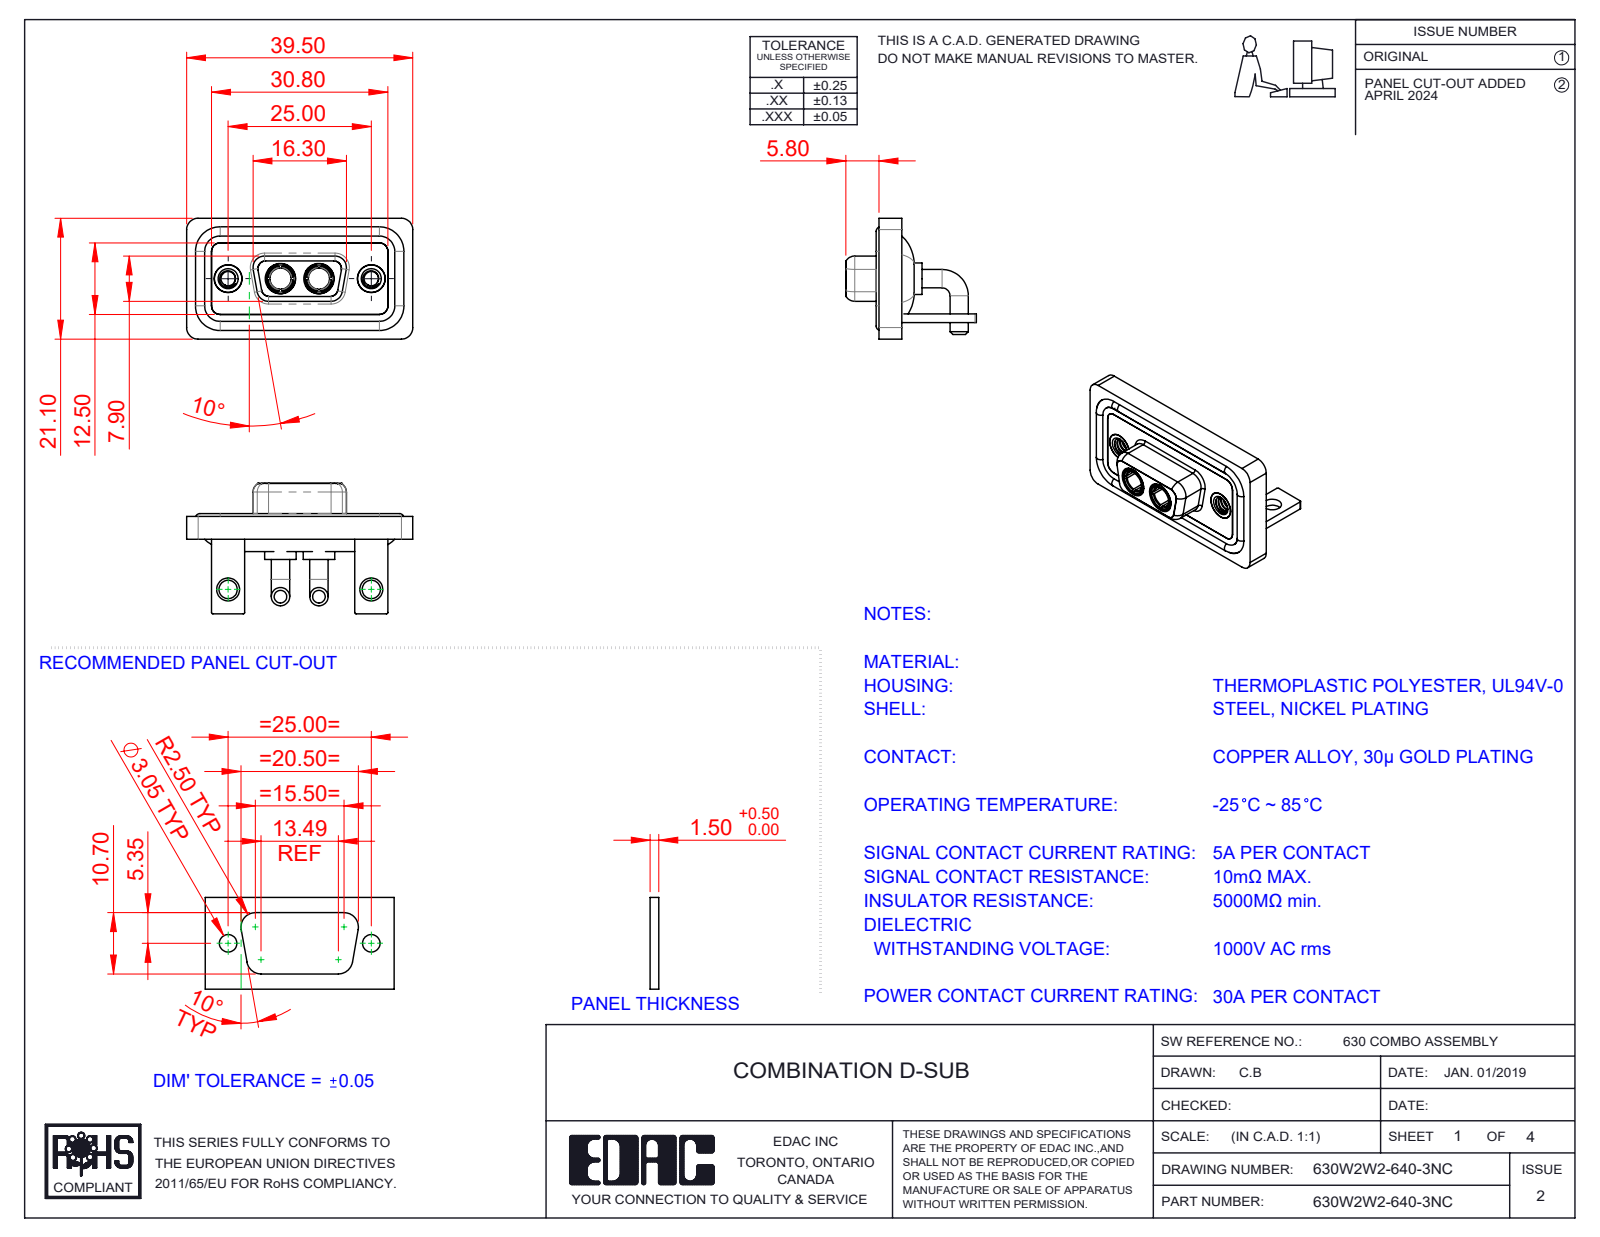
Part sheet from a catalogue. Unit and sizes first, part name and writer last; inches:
Units: inches
Overall size (bounding box): 1.555 × 0.898 × 0.831
Round holes (diameter × count): ⌀0.191 ×4, ⌀0.098 ×2, ⌀0.126 ×2, ⌀0.146 ×2, ⌀0.157 ×2, ⌀0.159 ×2, ⌀0.197 ×2, ⌀0.209 ×2
Round bosses / shafts (diameter × count): ⌀0.126 ×4, ⌀0.063 ×4, ⌀0.217 ×2, ⌀0.205 ×2, ⌀0.195 ×2, ⌀0.195 ×2, ⌀0.189 ×2, ⌀0.187 ×2
Partial cylindrical surfaces — rounded edges, fillets, slot ends (radius × count): R0.079 ×19, R0.059 ×18, R0.01 ×16, R0.053 ×8, R0.063 ×8, R0.02 ×5, R0.024 ×4, R0.026 ×4
Main face-to-face distances: 0.016, 0.114, 0.059, 0.071, 0.043, 0.146, 0.031, 0.098, 0.063, 0.122
Hole centre spacings: 0.36, 0.624, 0.984, 0.265
Volume: 0.319 in³ · Surface area: 13.27 in²
Bodies: 13 solids, 584 faces (183 planar, 260 cylindrical, 141 other)
Part name (STEP PRODUCT): 630Combo Shell Front_09 Contacts; 630Combo Shell Rear_09 Contacts; Power Socket_30A RA; 630Combo Waterproof Housing_09 Contacts (+4 more)
STEP written by: SolidWorks 2023 (CONFIG_CONTROL_DESIGN)
